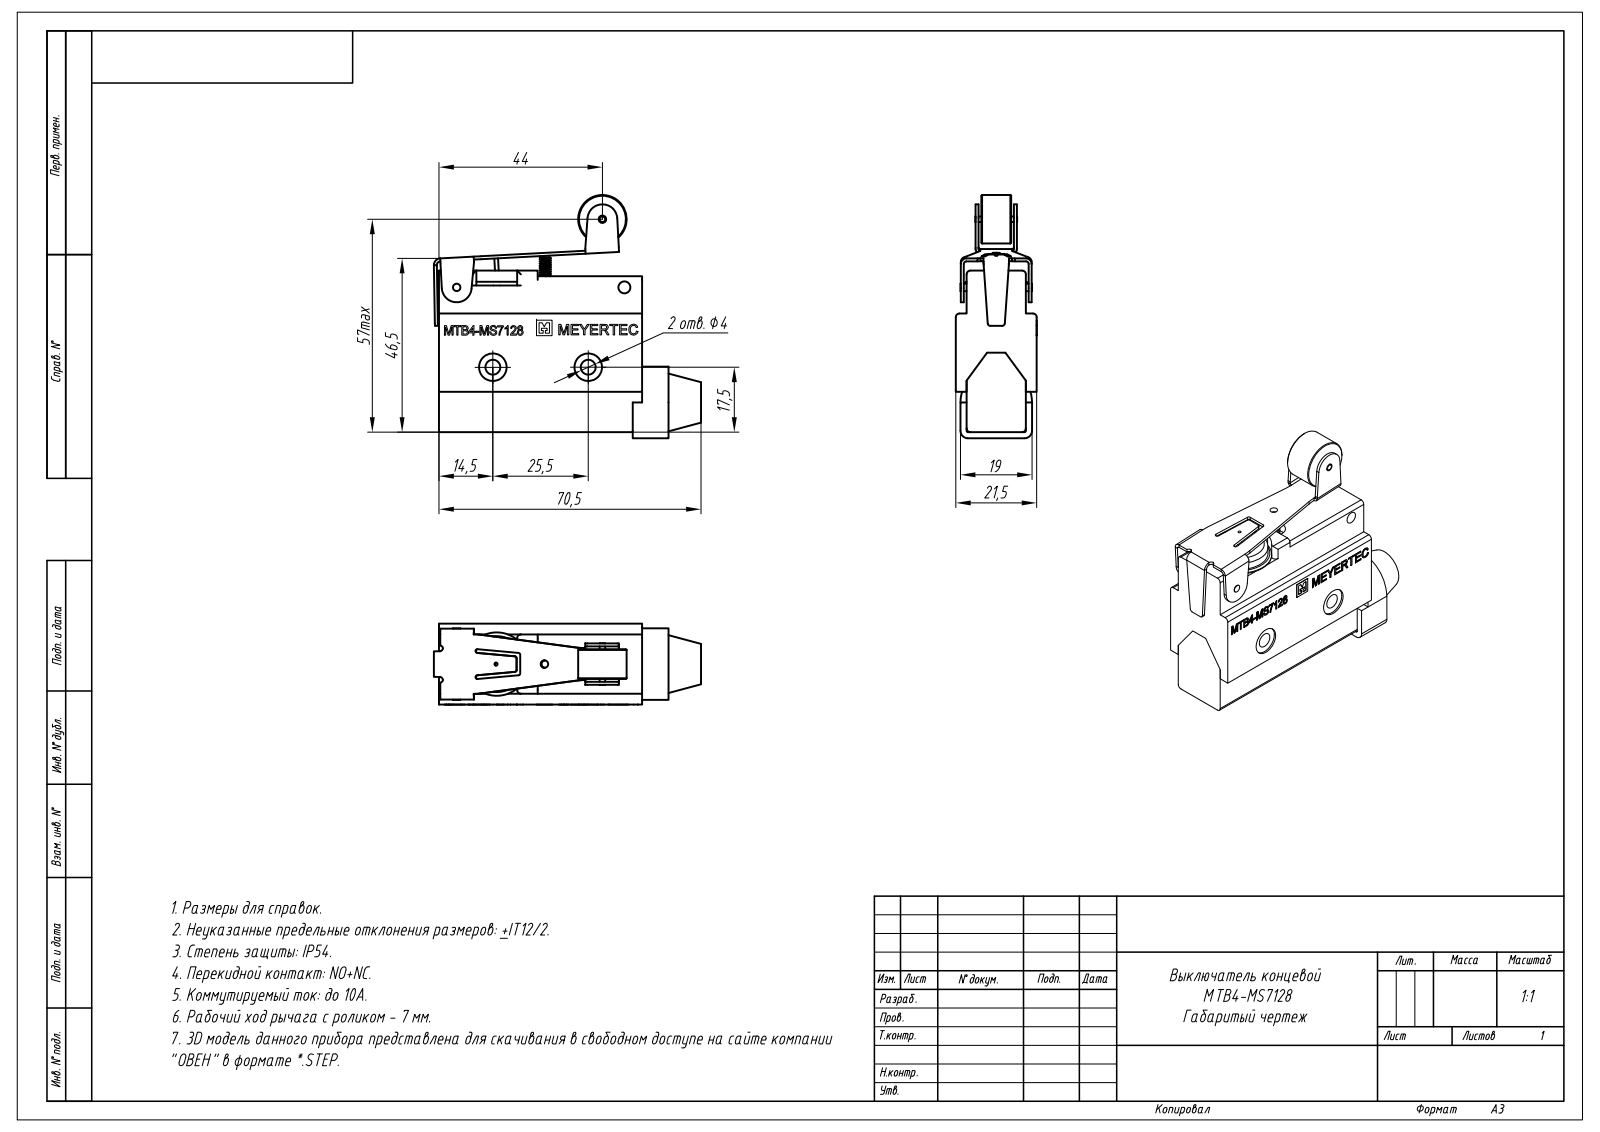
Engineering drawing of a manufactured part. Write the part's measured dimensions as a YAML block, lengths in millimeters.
part_name: "MTB4-MS7128"
step_written_by: "C3D Toolkit (CONFIG_CONTROL_DESIGN)"
units: millimeters
bodies: {solids: 2, faces: 256, planar: 129, cylindrical: 92, other: 35}
overall_size: [72.08, 60.65, 22]
volume: 44236
surface_area: 13558
round_holes:
  - {diameter: 3.2, count: 2}
  - {diameter: 4.2, count: 2}
  - {diameter: 7.5, count: 2}
  - {diameter: 2.5, count: 1}
round_bosses_or_shafts:
  - {diameter: 4, count: 3}
  - {diameter: 3, count: 2}
  - {diameter: 2.8, count: 2}
  - {diameter: 15, count: 1}
  - {diameter: 12.3, count: 1}
  - {diameter: 3.5, count: 1}
  - {diameter: 2.5, count: 1}
partial_cylinders:
  - {radius: 1, count: 27}
  - {radius: 0.5, count: 11}
  - {radius: 0.2, count: 4}
  - {radius: 0.8, count: 4}
  - {radius: 1.8, count: 4}
  - {radius: 1.5, count: 3}
  - {radius: 0.85, count: 2}
  - {radius: 4, count: 2}
face_to_face_distances: [19, 3, 1, 16, 22, 4.5, 0.5, 43.8, 42.8, 5.5]
hole_center_spacings: [19.57, 19.76, 25.6, 39.18, 39.4, 45.2]
